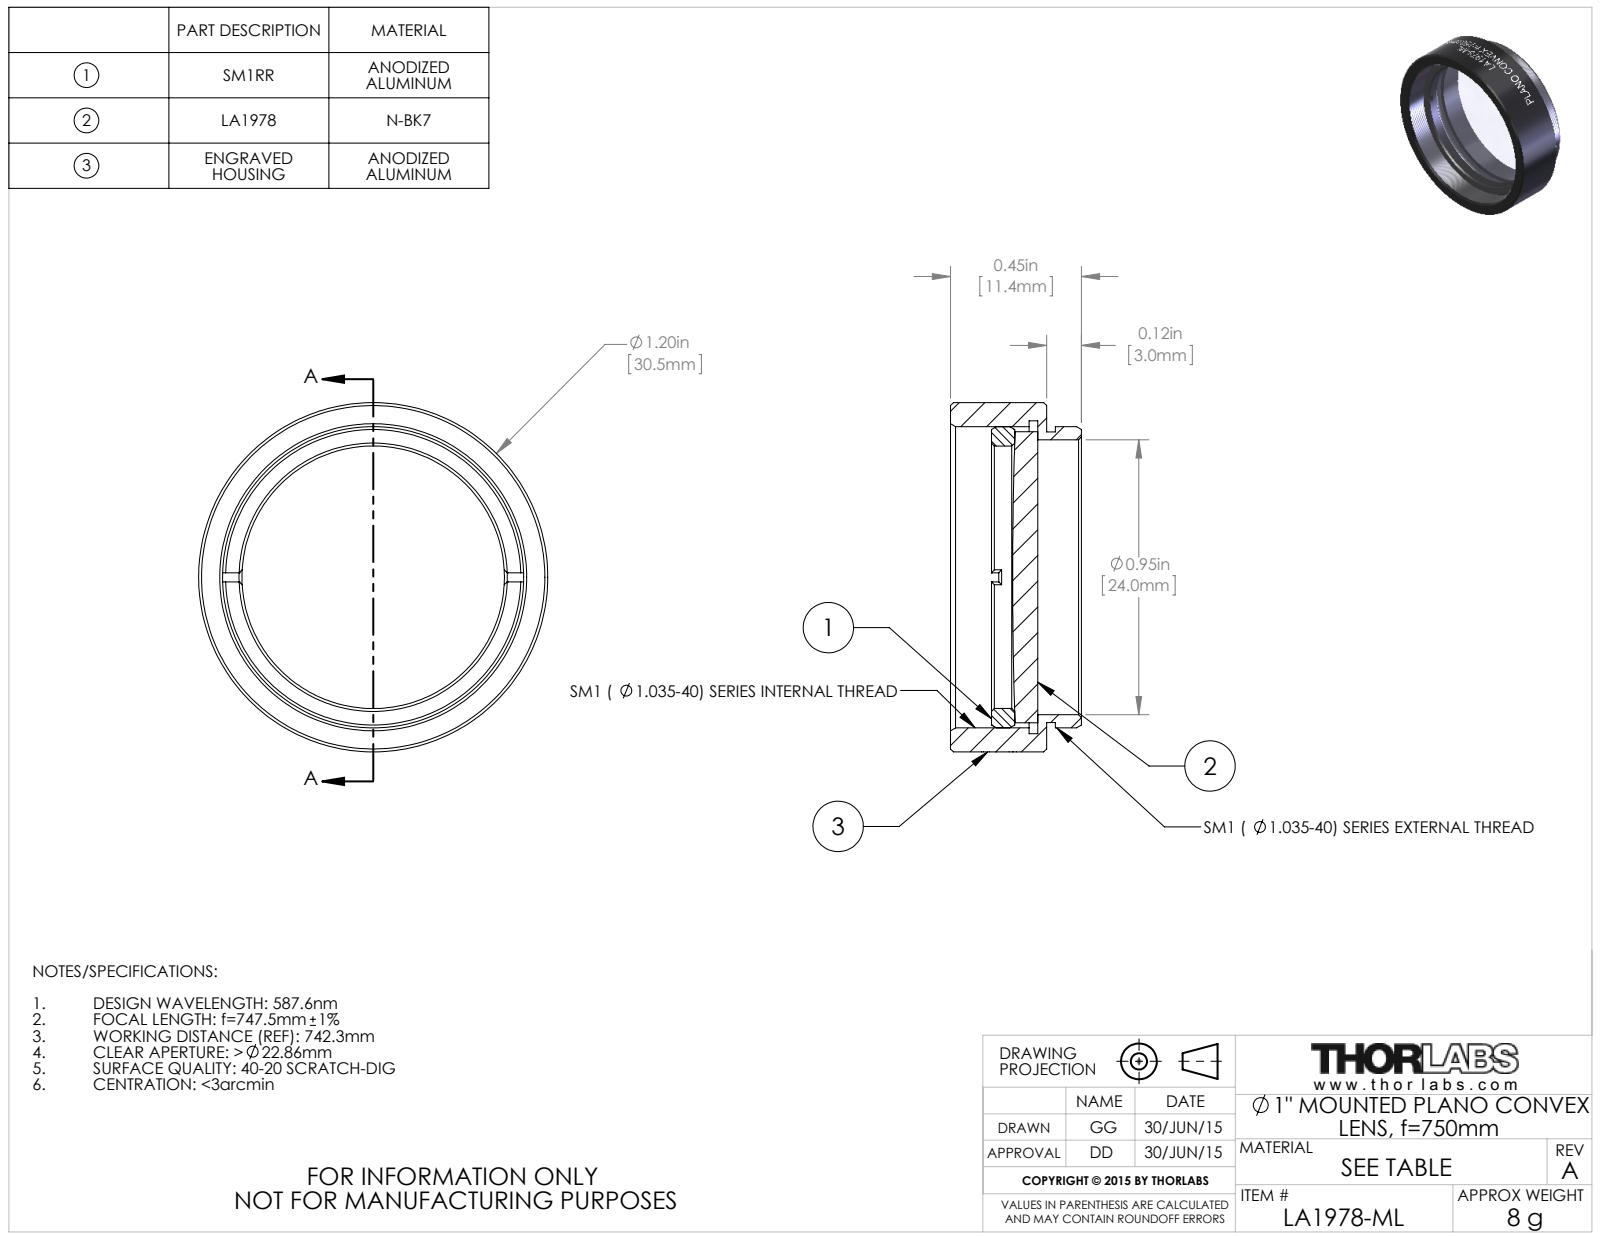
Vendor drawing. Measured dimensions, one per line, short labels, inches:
name: TTN039654-E0W
written by: SolidWorks 2014 (CONFIG_CONTROL_DESIGN)
unit: in
bodies: 3 solids, 119 faces (20 planar, 75 cylindrical, 24 other)
size: 1.2 × 1.2 × 0.45
volume: 0.192 in³; area: 6.684 in²
holes: 1× ⌀0.902, 1× ⌀0.945, 1× ⌀1.075
bosses: 1× ⌀1.2, 1× ⌀1.035, 1× ⌀1, 1× ⌀0.999
face distances: 0.03, 0.08, 0.03, 0.33, 0.3, 0.3, 0.11, 0.08, 0.22, 0.19
